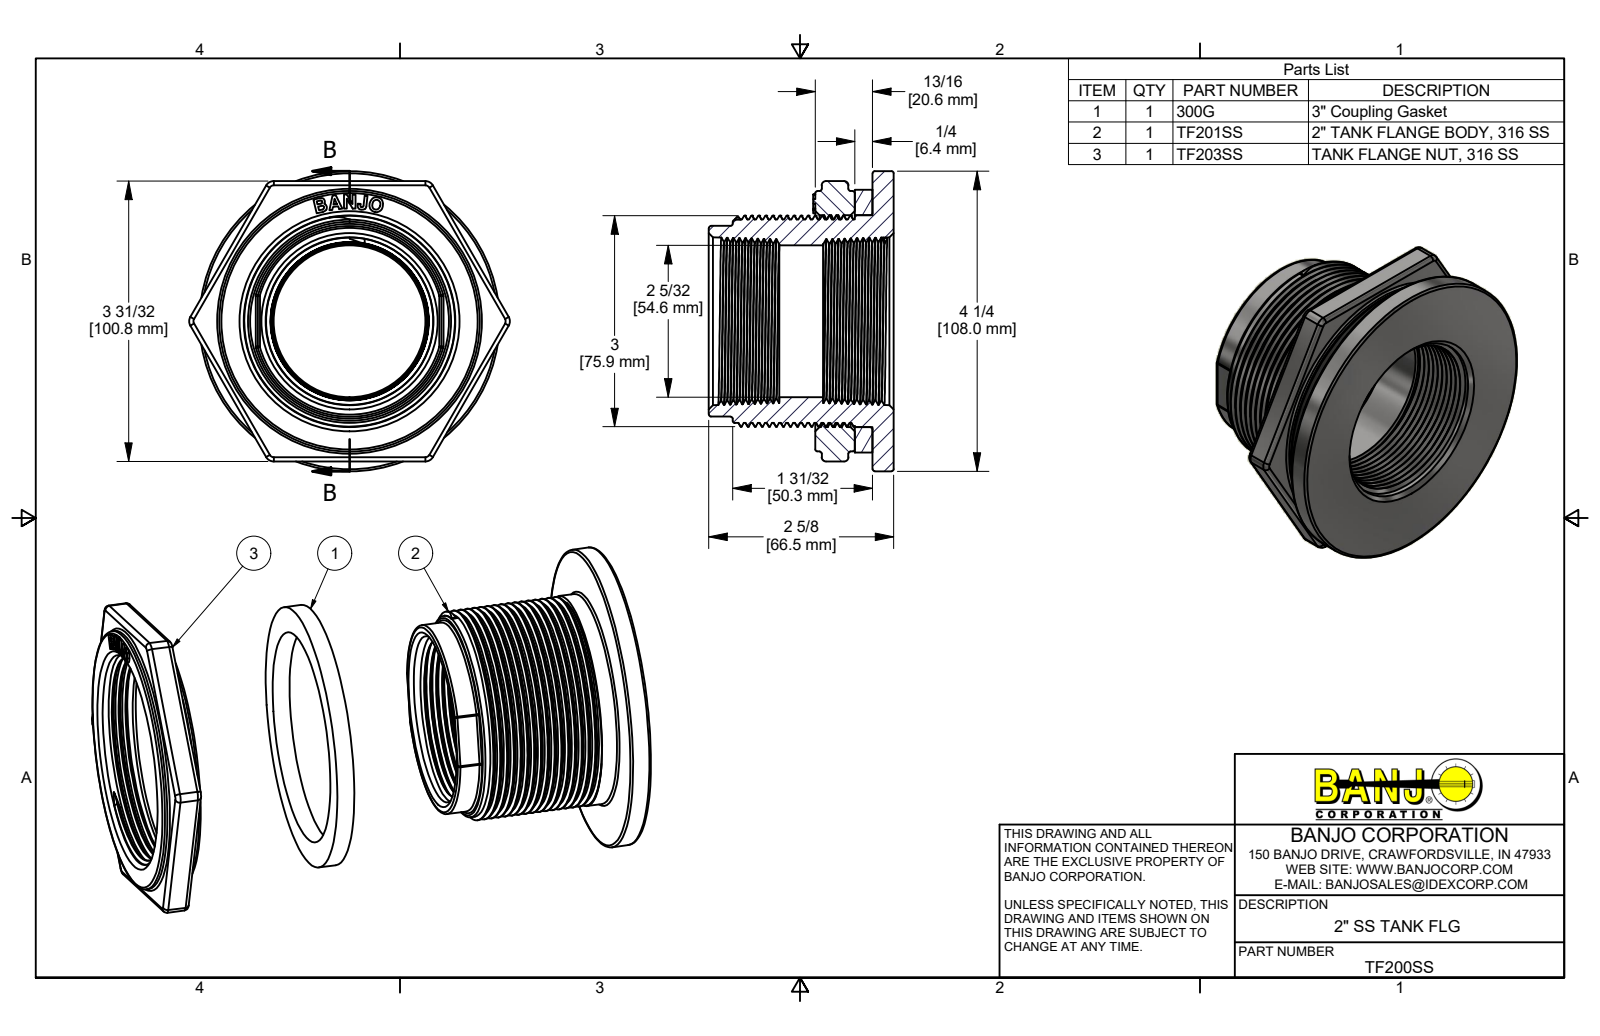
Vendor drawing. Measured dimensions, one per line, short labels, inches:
name: TF200SS; TF201SS; TF203SS; 300G
written by: Autodesk Inventor 2019 (AUTOMOTIVE_DESIGN)
unit: in
bodies: 3 solids, 262 faces (72 planar, 85 cylindrical, 105 other)
size: 73.923 × 4.544 × 4.25
volume: 12.16 in³; area: 667.7 in²
holes: 1× ⌀2.15, 1× ⌀2.892, 1× ⌀3
bosses: 1× ⌀4.25, 1× ⌀3.719, 1× ⌀3.687, 1× ⌀2.987, 1× ⌀2.879, 1× ⌀2.7
rounds: 16× R0.06, 6× R0.125, 4× R0.03, 1× R0.5
face distances: 0.3, 0.25, 0.55, 0.094, 0.469, 0.563, 0.813, 1.113, 0.719, 1.019
